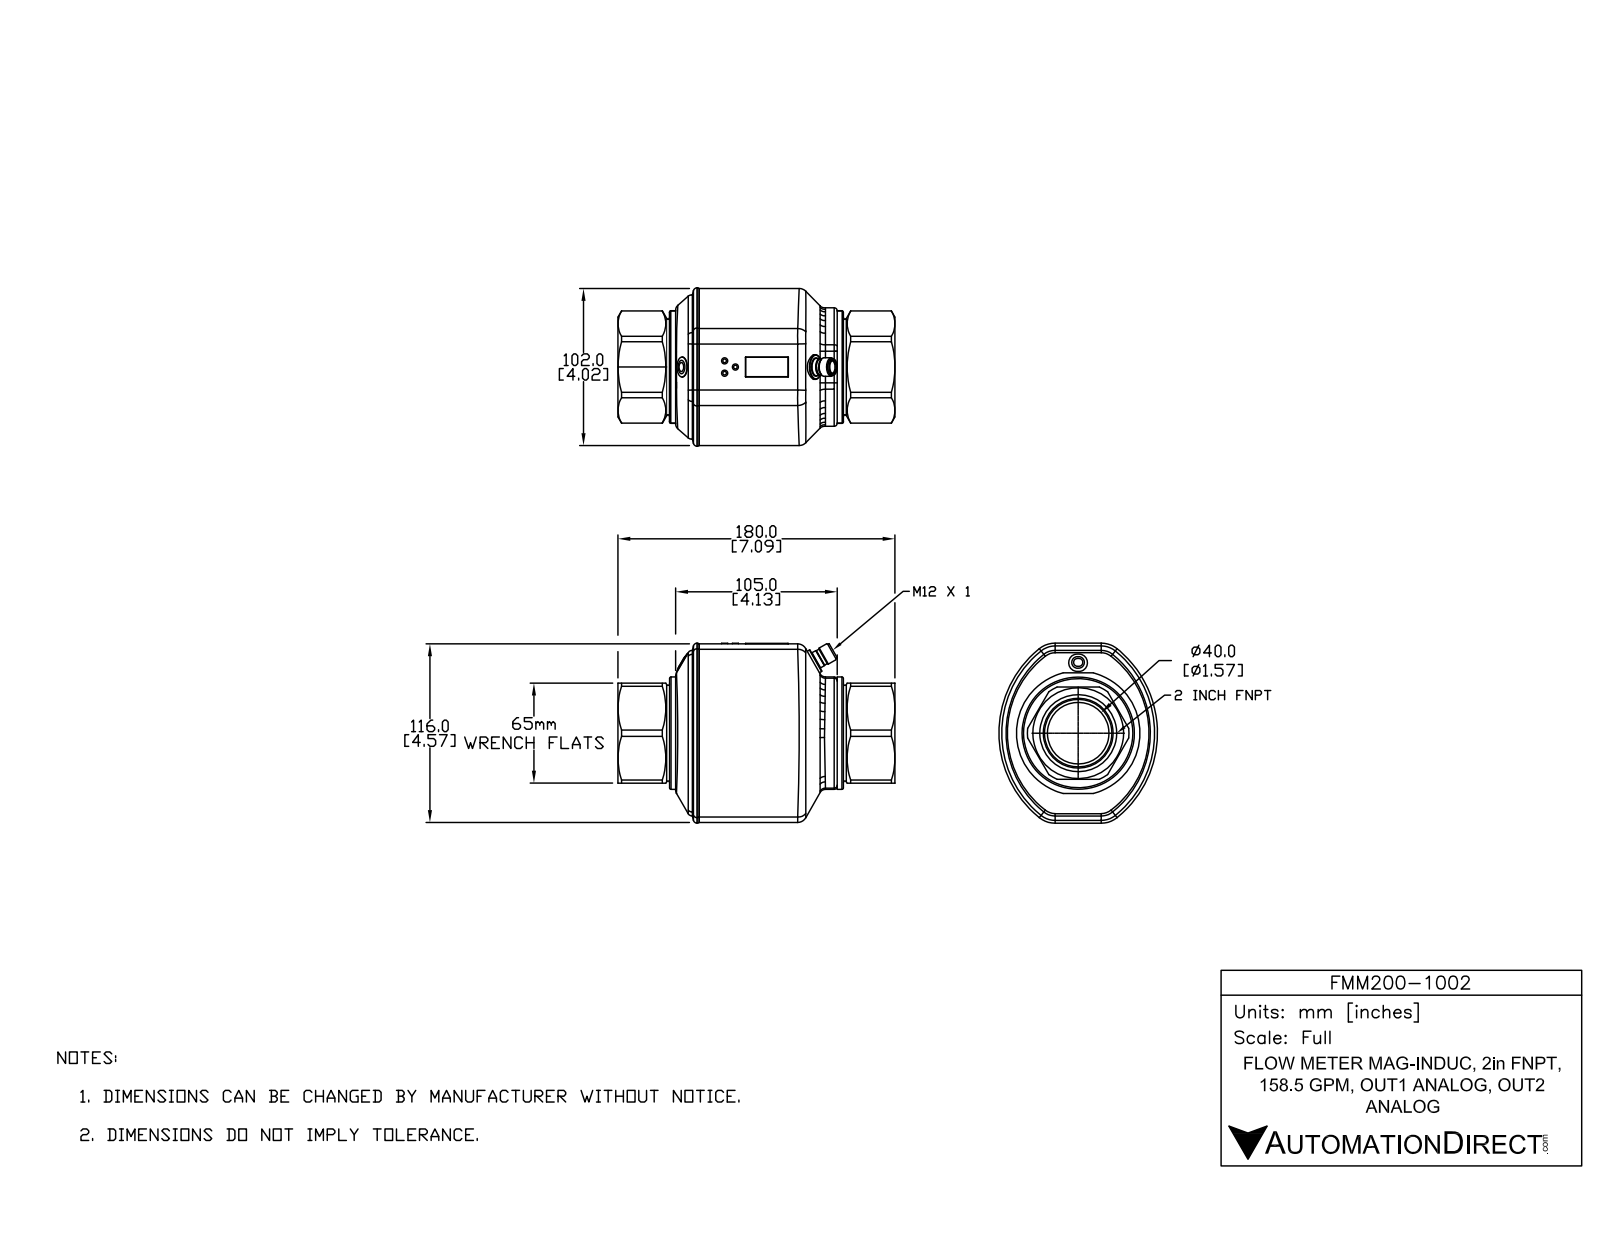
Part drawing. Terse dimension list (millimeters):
name: FMM200-1002
written by: SolidWorks 2015 (AUTOMOTIVE_DESIGN)
unit: mm
bodies: 10 solids, 289 faces (81 planar, 84 cylindrical, 124 other)
size: 186.28 × 118.91 × 103
volume: 1 085 000 mm³; area: 125 550 mm²
holes: 1× ⌀8.4, 1× ⌀40, 1× ⌀56
bosses: 3× ⌀4, 2× ⌀12, 2× ⌀3.9, 1× ⌀73, 1× ⌀64, 1× ⌀14.9, 1× ⌀11.3, 1× ⌀10.6
rounds: 4× R0.9, 4× R11, 4× R16, 4× R16.5, 2× R1, 2× R2, 2× R70, 2× R70.5
face distances: 23.91, 79.3, 103.21, 110.88, 31.58, 7.67, 65, 25.5, 90.5, 4.87
